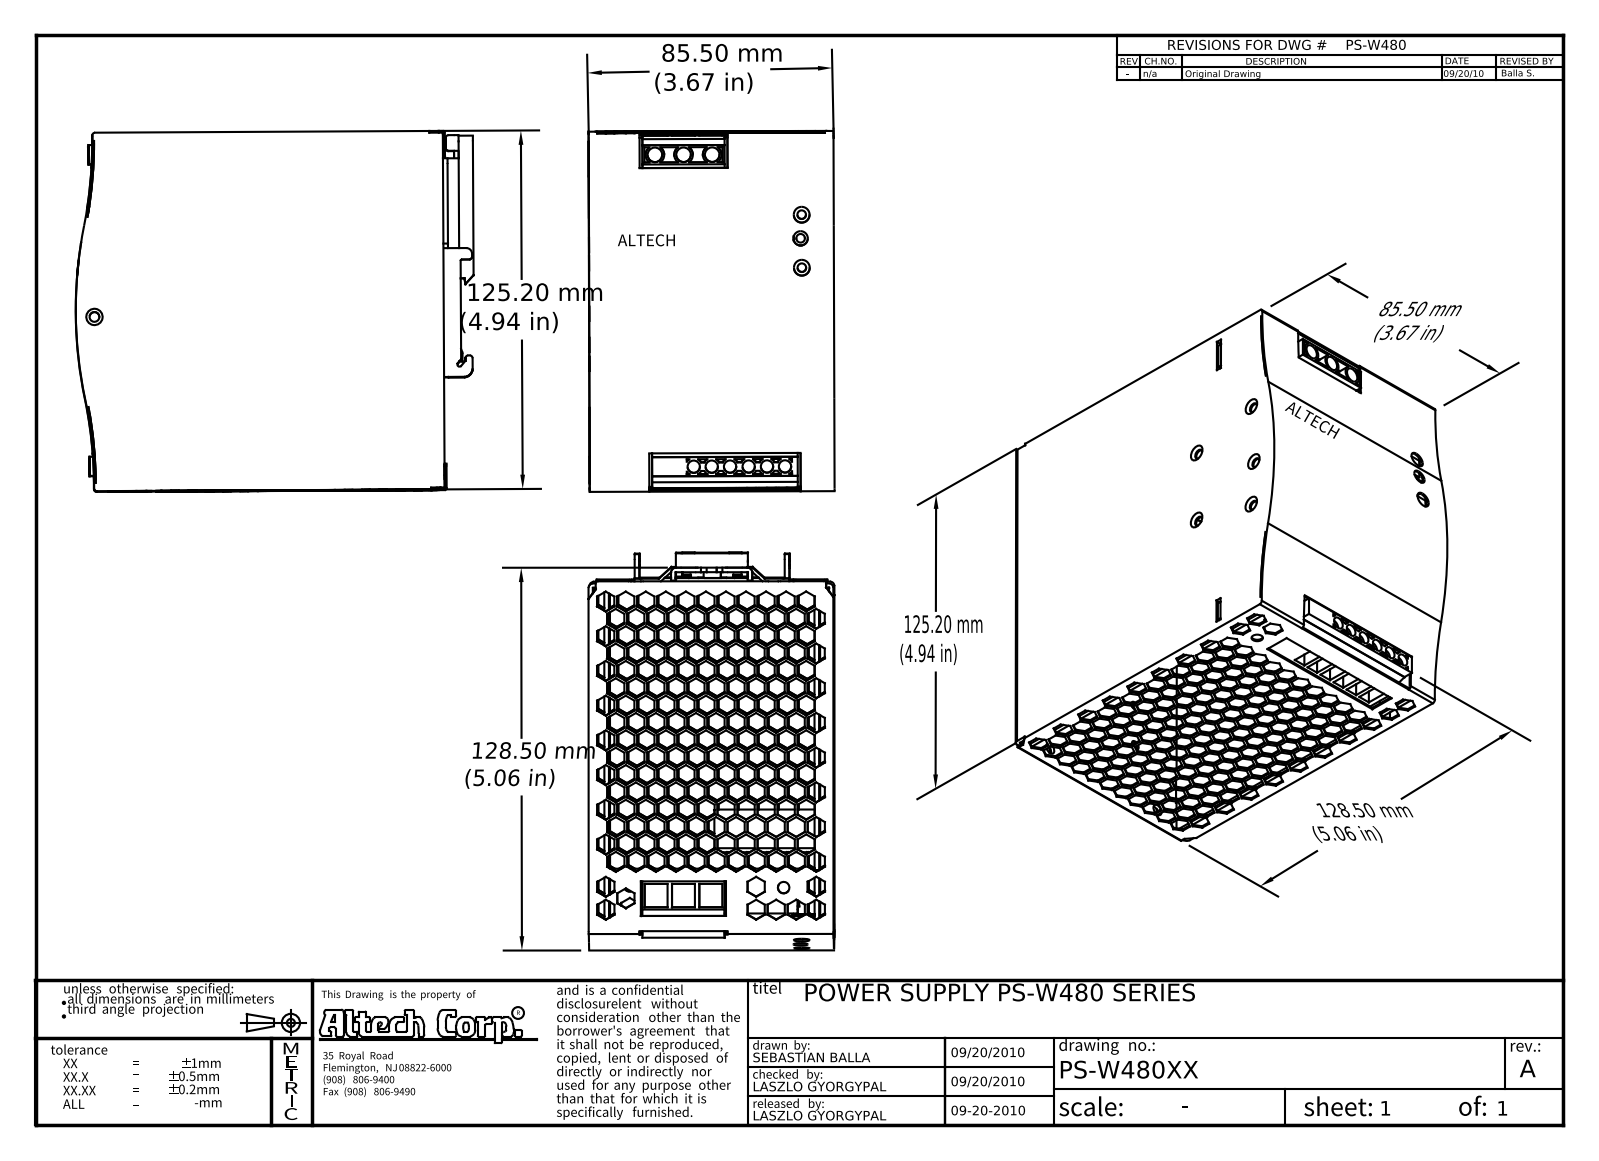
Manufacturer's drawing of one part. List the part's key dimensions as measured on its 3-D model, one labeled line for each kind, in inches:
Part name (STEP PRODUCT): PS-W480; Y2STRIP-TOP; YSTRIP-BOTTOM; INNER (+1 more)
STEP written by: Autodesk Inventor 2008 (AUTOMOTIVE_DESIGN)
Units: inches
Bodies: 4 solids, 2899 faces (2720 planar, 162 cylindrical, 17 other)
Overall size (bounding box): 5.472 × 4.929 × 3.366
Volume: 11.62 in³ · Surface area: 351 in²
Round holes (diameter × count): ⌀0.134 ×11, ⌀0.157 ×6, ⌀0.169 ×6, ⌀0.102 ×3, ⌀0.201 ×3, ⌀0.118 ×2, ⌀0.217 ×2, ⌀0.138 ×1, ⌀0.197 ×1
Round bosses / shafts (diameter × count): ⌀0.531 ×6, ⌀0.118 ×1
Partial cylindrical surfaces — rounded edges, fillets, slot ends (radius × count): R0.039 ×19, R0.079 ×11, R0.02 ×8, R0.118 ×7, R0.004 ×6, R0.067 ×5, R0.069 ×4, R0.128 ×3
Main face-to-face distances: 0.063, 0.059, 3.307, 2.89, 0.138, 0.197, 3.366, 3.248, 0.26, 3.11
Hole centre spacings: 0.658, 0.248, 0.252, 0.394, 0.5, 0.508, 0.756, 0.969
